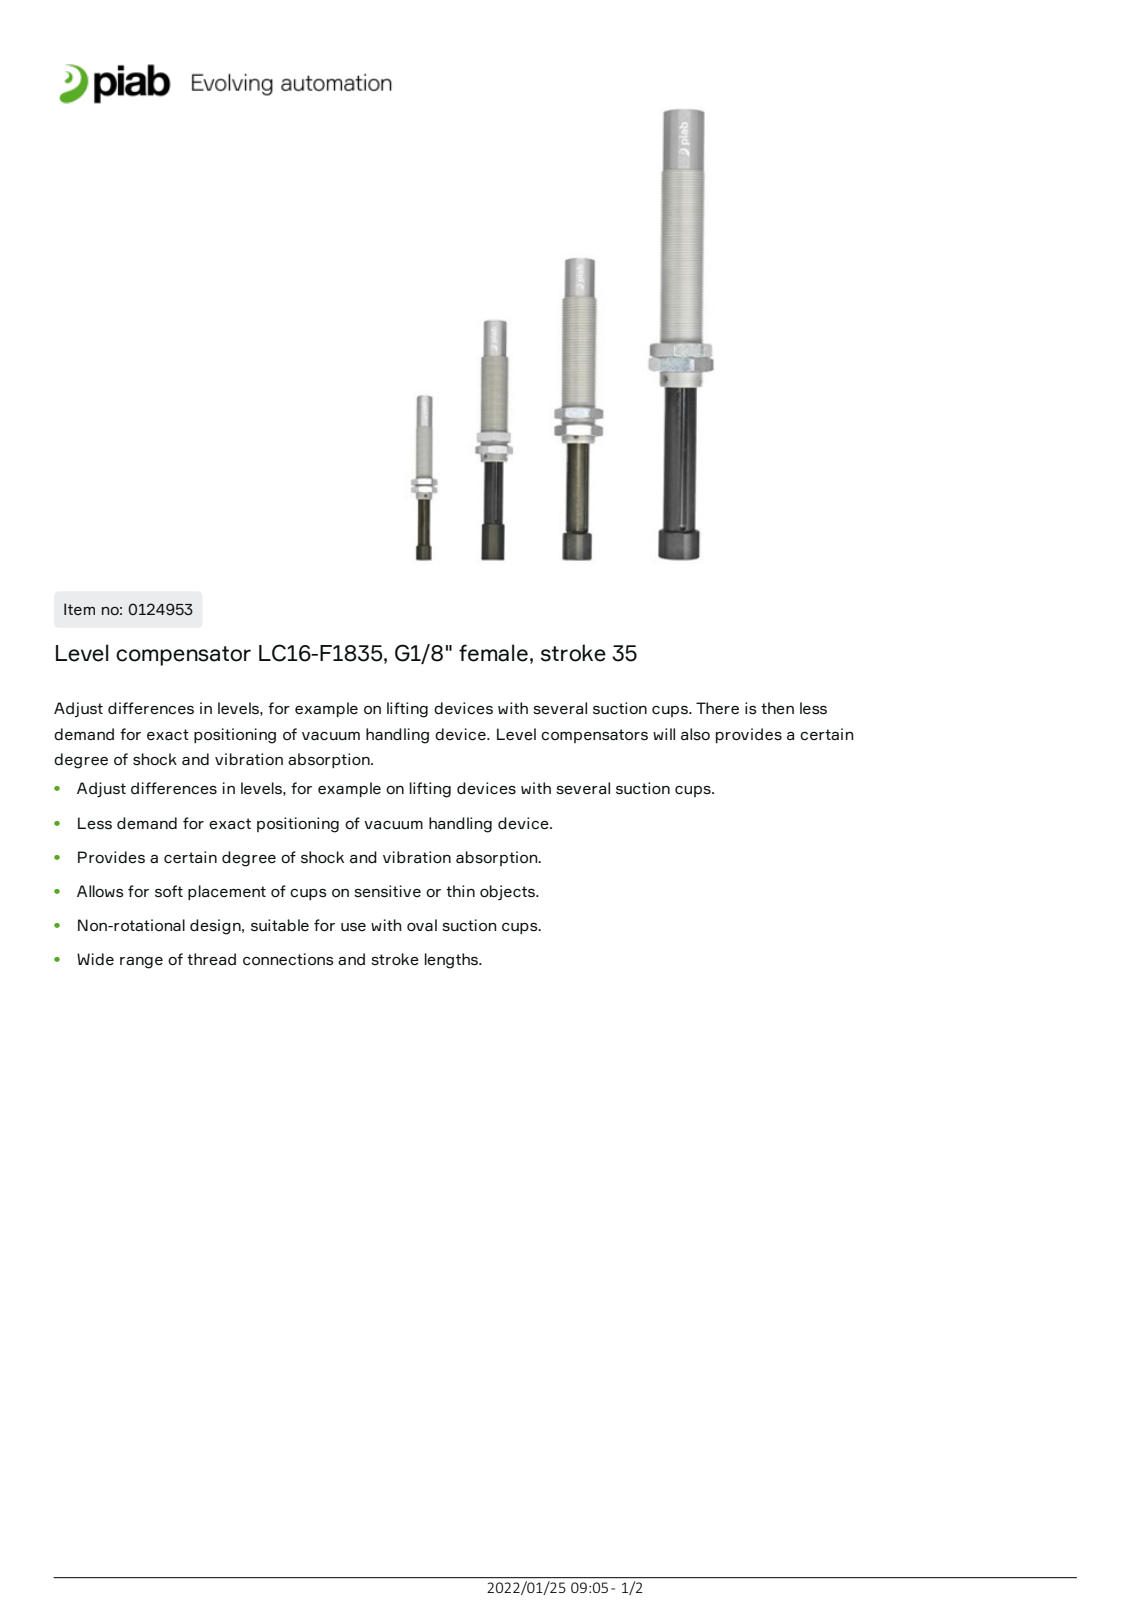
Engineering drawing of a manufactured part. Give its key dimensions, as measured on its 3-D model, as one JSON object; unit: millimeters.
{"part_name": "Nut M16x1; Body threaded; Rod vacuum; Piab adaptor nut G18 (+1 more)", "step_written_by": "Unknown (automotive_design)", "units": "millimeters", "bodies": {"solids": 11, "faces": 159, "planar": 74, "cylindrical": 49, "other": 36}, "overall_size": [135, 32.47, 21.94], "volume_mm3": 33225, "surface_area_mm2": 28242, "round_holes": [[6, 2], [8.7, 2], [15, 2], [4.2, 1], [10.7, 1]], "round_bosses_or_shafts": [[16, 1], [8, 1]], "partial_cylinders_radius": [[6.4, 2]], "face_to_face_distances": [12, 15.5, 3.5, 6, 5, 19, 11, 1, 7, 58.5]}
